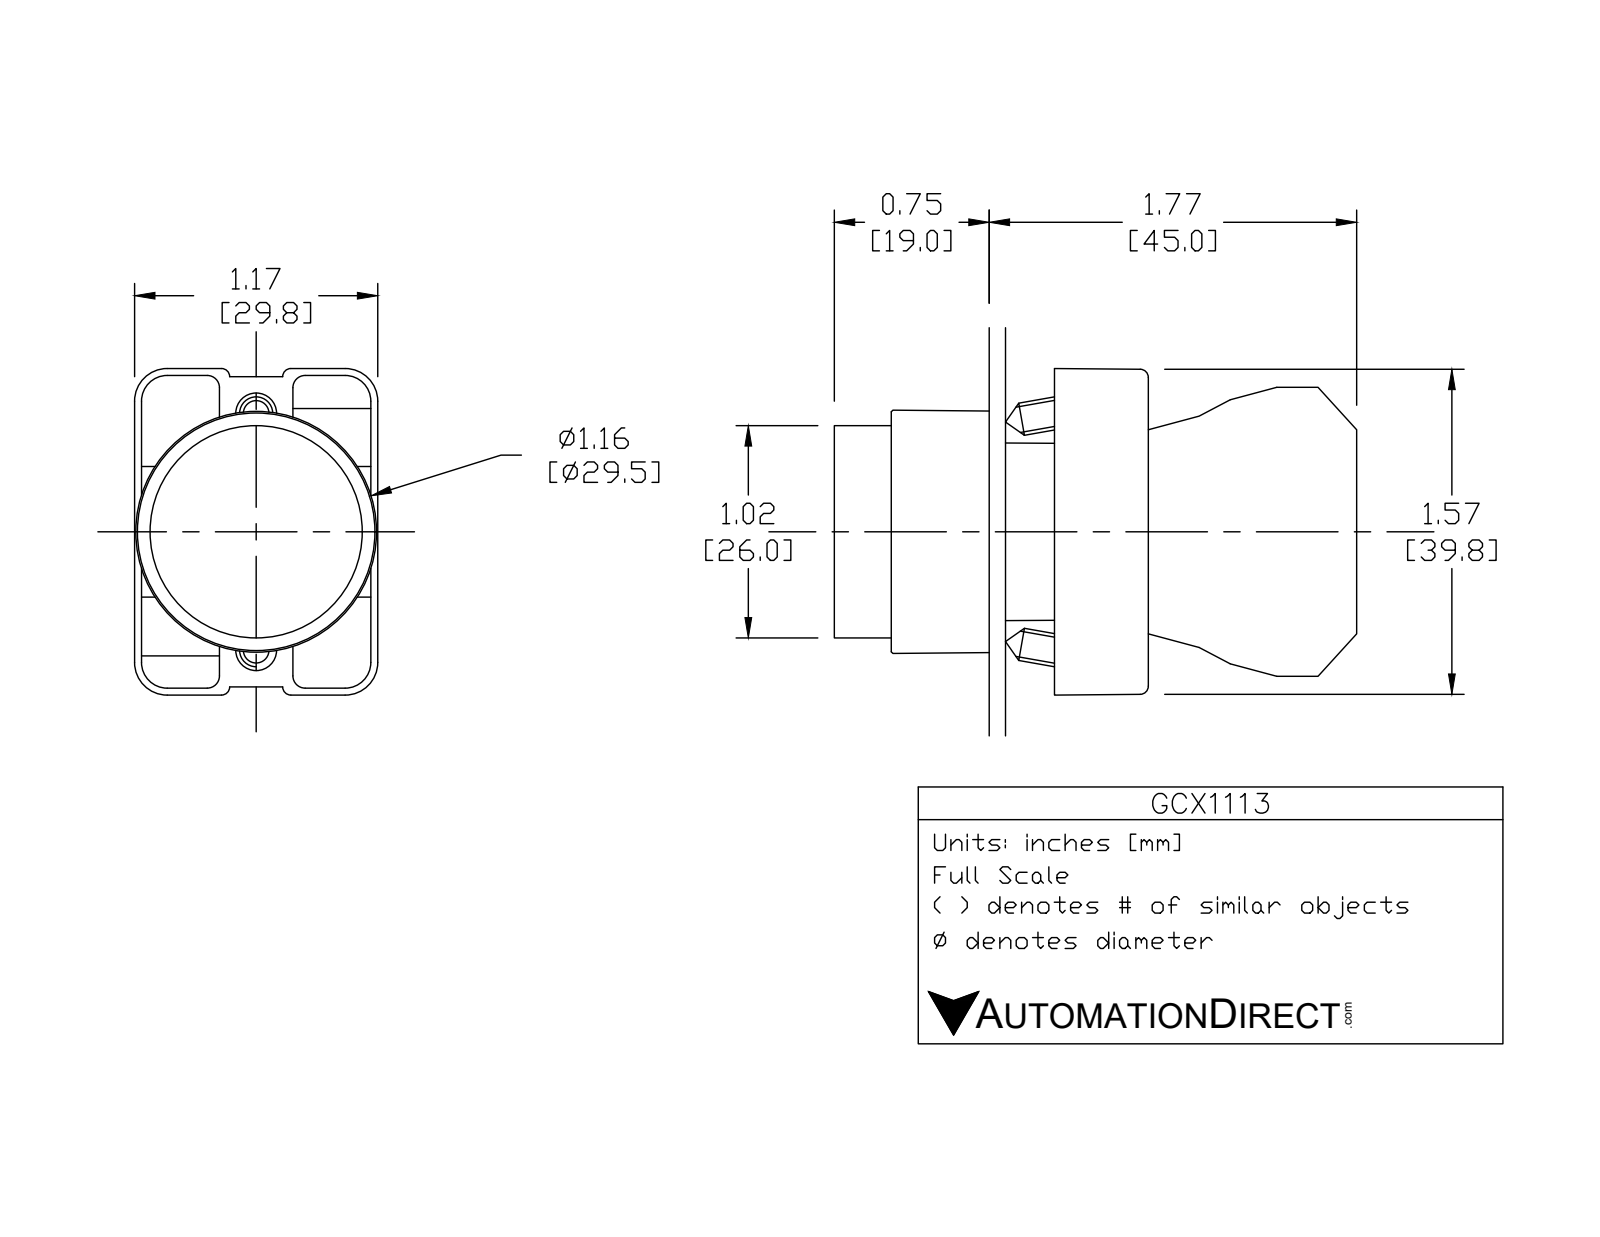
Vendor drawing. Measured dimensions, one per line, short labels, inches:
name: GCX1113 OPERATOR; ecx1040; ecx1029; GCX1113
written by: SolidWorks 2016 (AUTOMOTIVE_DESIGN)
unit: in
bodies: 6 solids, 383 faces (222 planar, 132 cylindrical, 29 other)
size: 2.492 × 1.581 × 1.177
volume: 1.584 in³; area: 26.47 in²
holes: 2× ⌀0.079, 2× ⌀0.124, 2× ⌀0.13, 1× ⌀0.087, 1× ⌀0.197, 1× ⌀0.878, 1× ⌀0.888, 1× ⌀1.024
bosses: 2× ⌀0.157, 1× ⌀1.175, 1× ⌀1.004, 1× ⌀0.945, 1× ⌀0.856, 1× ⌀0.78
rounds: 24× R0.059, 12× R0.041, 12× R0.124, 12× R0.157, 4× R0.039, 2× R0.128, 1× R0.02, 1× R0.063
face distances: 0.579, 0.033, 1.193, 0.031, 0.472, 0.72, 0.276, 0.689, 0.598, 1.161
hole spacings: 0.236, 0.544, 0.472, 0.49
